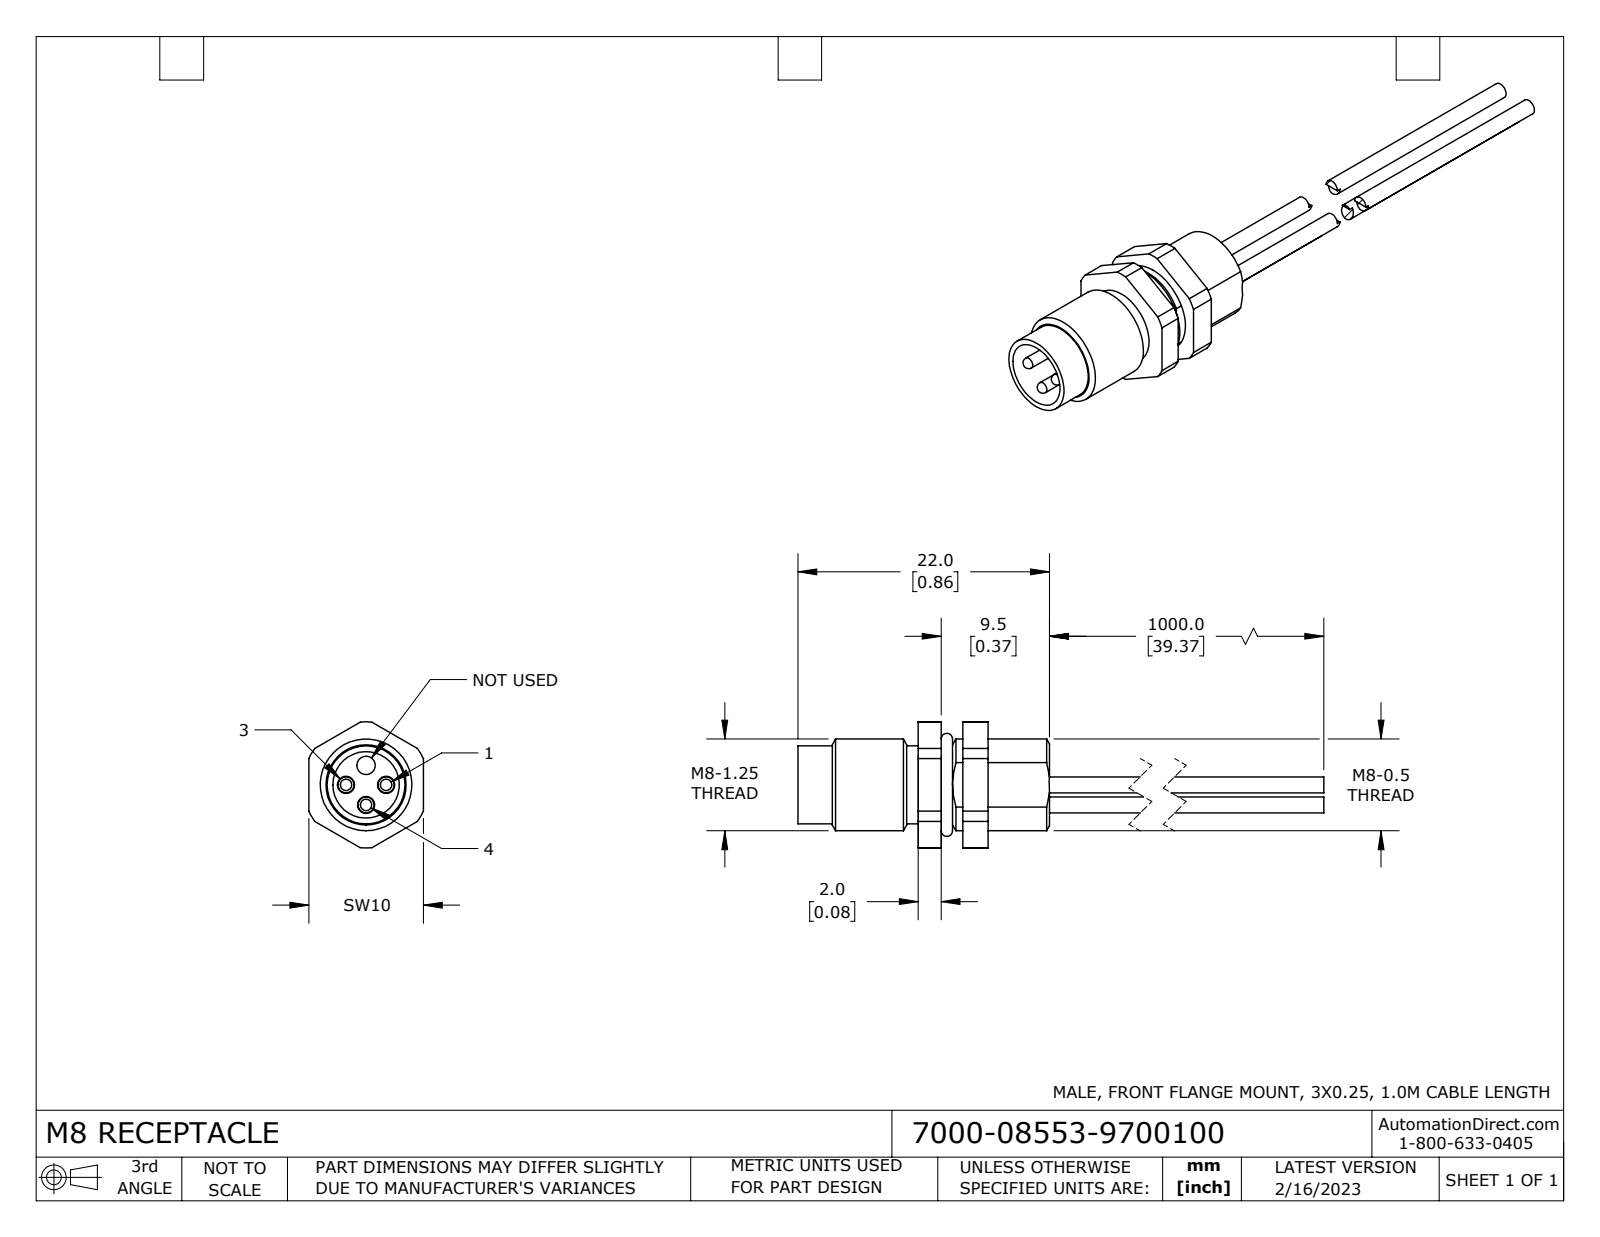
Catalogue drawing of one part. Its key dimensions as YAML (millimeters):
part_name: "7000-08553-9700100"
step_written_by: "SolidWorks 2021 (CONFIG_CONTROL_DESIGN)"
units: millimeters
bodies: {solids: 9, faces: 107, planar: 34, cylindrical: 51, other: 22}
overall_size: [120, 11, 10]
volume: 1400
surface_area: 2761
round_holes:
  - {diameter: 1.5, count: 3}
  - {diameter: 1.6, count: 1}
  - {diameter: 5.8, count: 1}
  - {diameter: 6.2, count: 1}
round_bosses_or_shafts:
  - {diameter: 1.4, count: 3}
  - {diameter: 1, count: 3}
  - {diameter: 8, count: 1}
  - {diameter: 6.8, count: 1}
partial_cylinders:
  - {radius: 5.5, count: 1}
face_to_face_distances: [10, 2, 7.5, 8.5, 1.5, 7, 1.9, 3.9, 2.2, 4.1]
hole_center_spacings: [1.8, 2.4, 2.5, 1.7, 3.5, 3.5]
